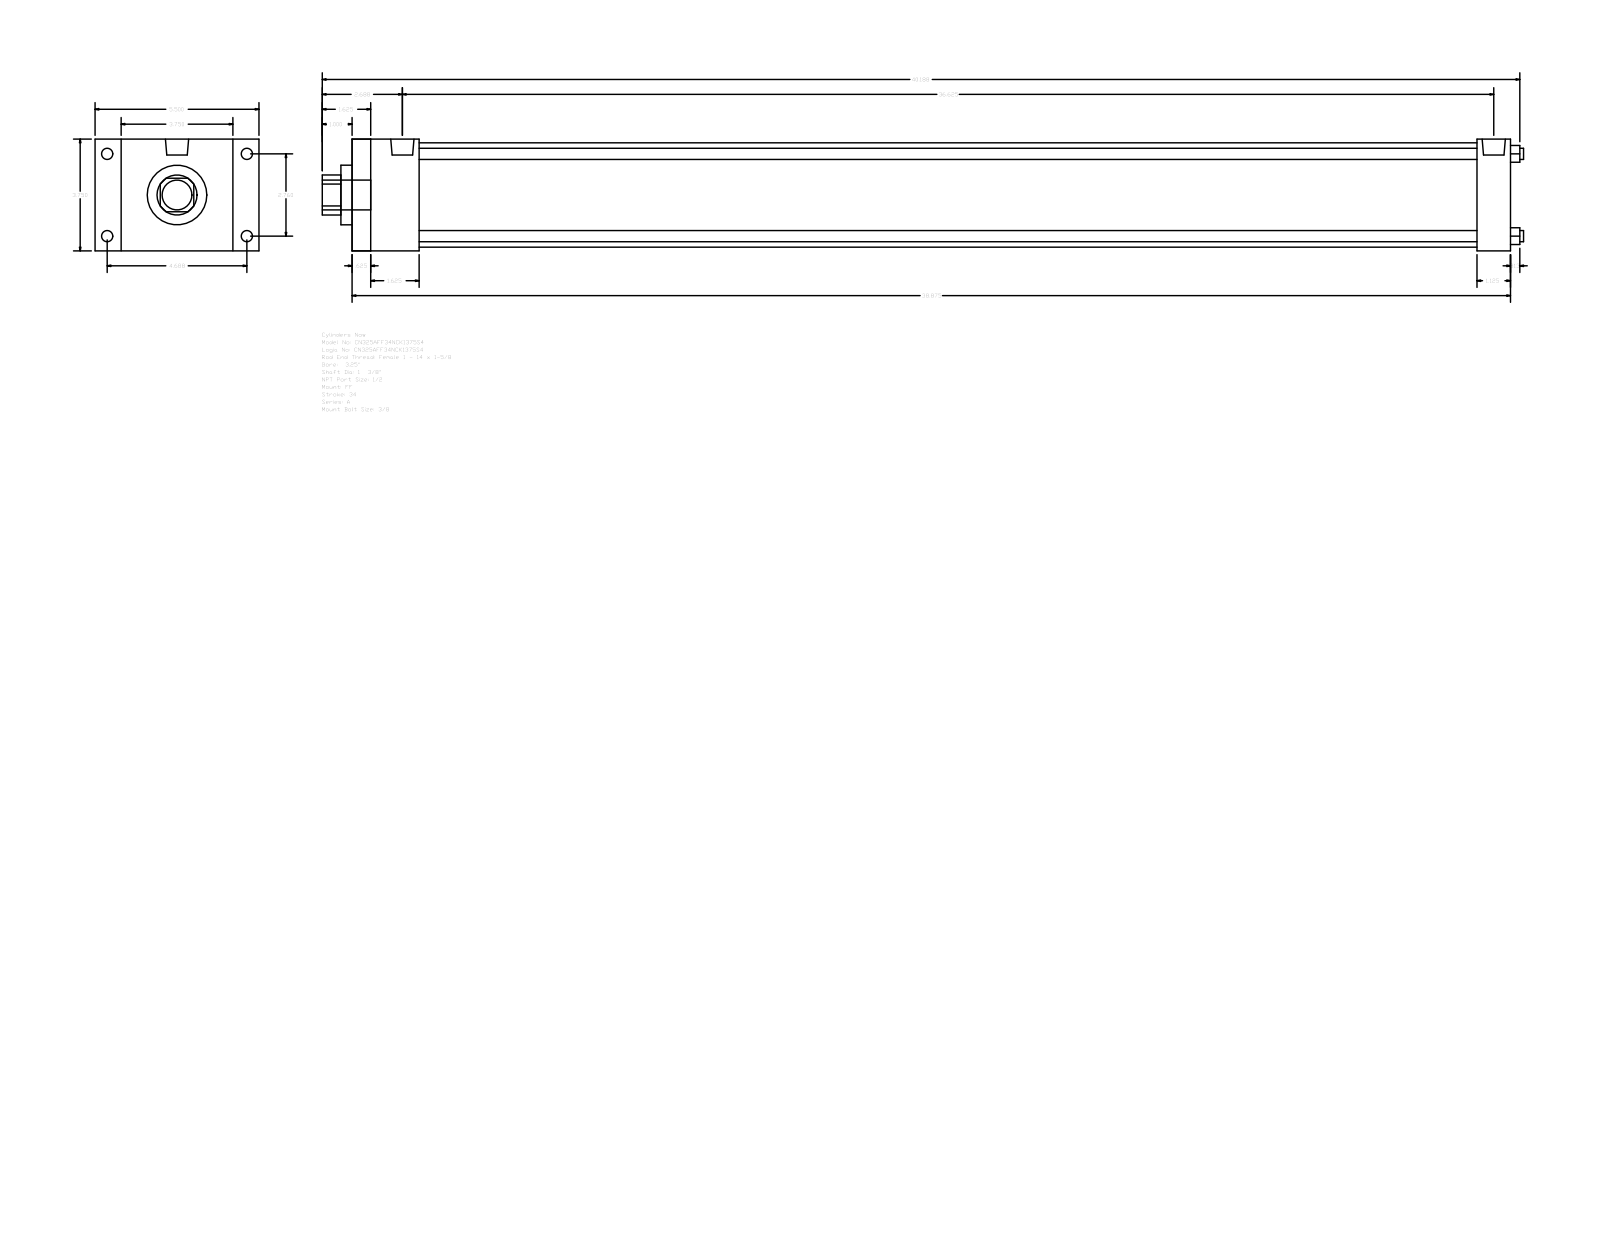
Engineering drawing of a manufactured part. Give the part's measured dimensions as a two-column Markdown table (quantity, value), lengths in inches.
| quantity | value |
| --- | --- |
| part name | A_FF__0325_1.375 |
| STEP written by | GSSL Pune (CONFIG_CONTROL_DESIGN) |
| units | inches |
| bodies | 0 solids, 92 faces (64 planar, 28 cylindrical, 0 other) |
| overall size | 40.313 × 5.5 × 3.75 |
| round holes (diameter × count) | 0.375 × 4, 1.375 × 1, 2 × 1, 3.5 × 1 |
| round bosses / shafts (diameter × count) | 0.375 × 4, 0.344 × 4, 0.778 × 2, 1 × 1 |
| partial cylindrical surfaces (radius × count) | 0.672 × 1 |
| main face-to-face distances | 3.75, 38.875, 0.625, 38.25, 1.125, 0.875, 4.625, 2.25, 37.75, 1.625 |
| hole center spacings | 1.952, 2.76, 3.903 |
